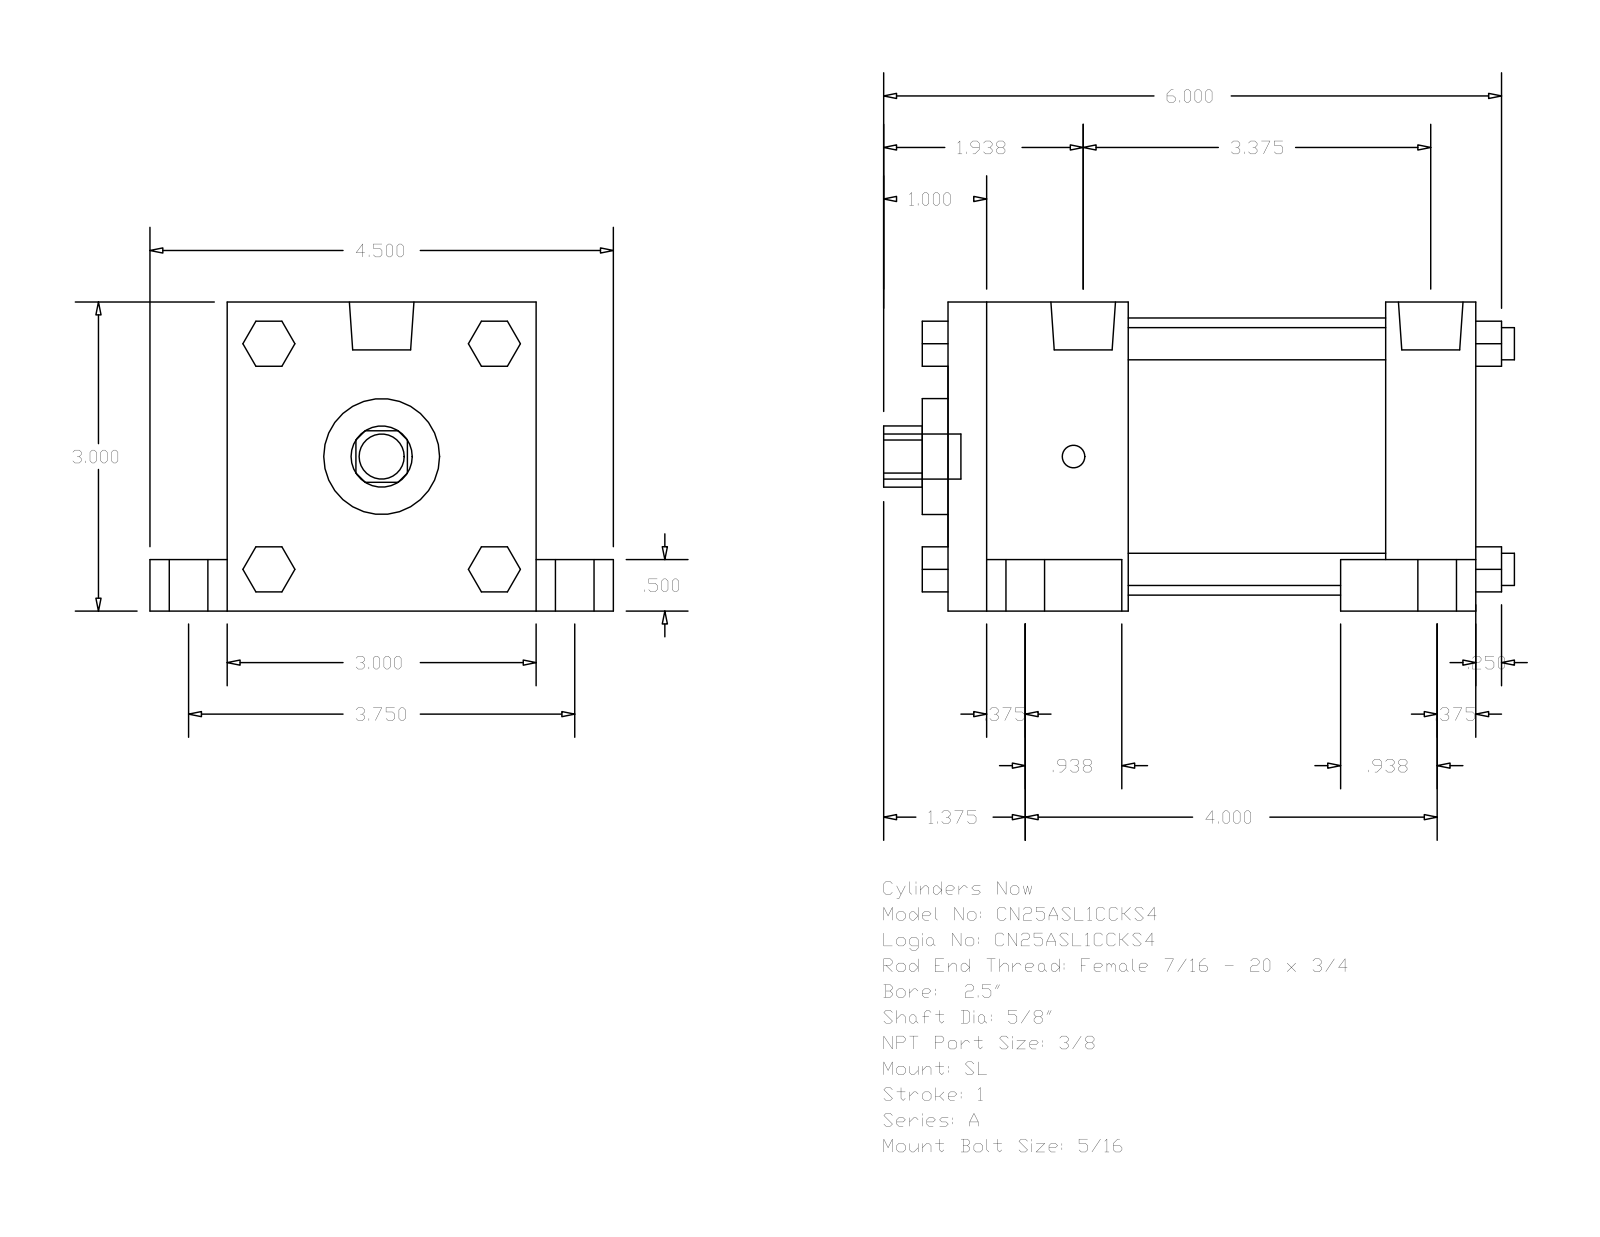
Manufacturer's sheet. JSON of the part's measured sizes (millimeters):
{"part_name": "A_SL__0250_0.625", "step_written_by": "GSSL Pune (CONFIG_CONTROL_DESIGN)", "units": "millimeters", "bodies": {"solids": 0, "faces": 148, "planar": 112, "cylindrical": 36, "other": 0}, "overall_size": [155.57, 114.3, 76.2], "round_holes": [[15.88, 1], [28.57, 1], [68.33, 1]], "round_bosses_or_shafts": [[15.88, 4], [9.53, 4], [7.94, 4], [5.56, 4], [15.93, 2], [11.11, 1]], "partial_cylinders_radius": [[7.54, 1]], "face_to_face_distances": [76.2, 130.17, 63.5, 44.45, 22.22, 85.72, 107.95, 12.7, 19.05, 95.25]}
